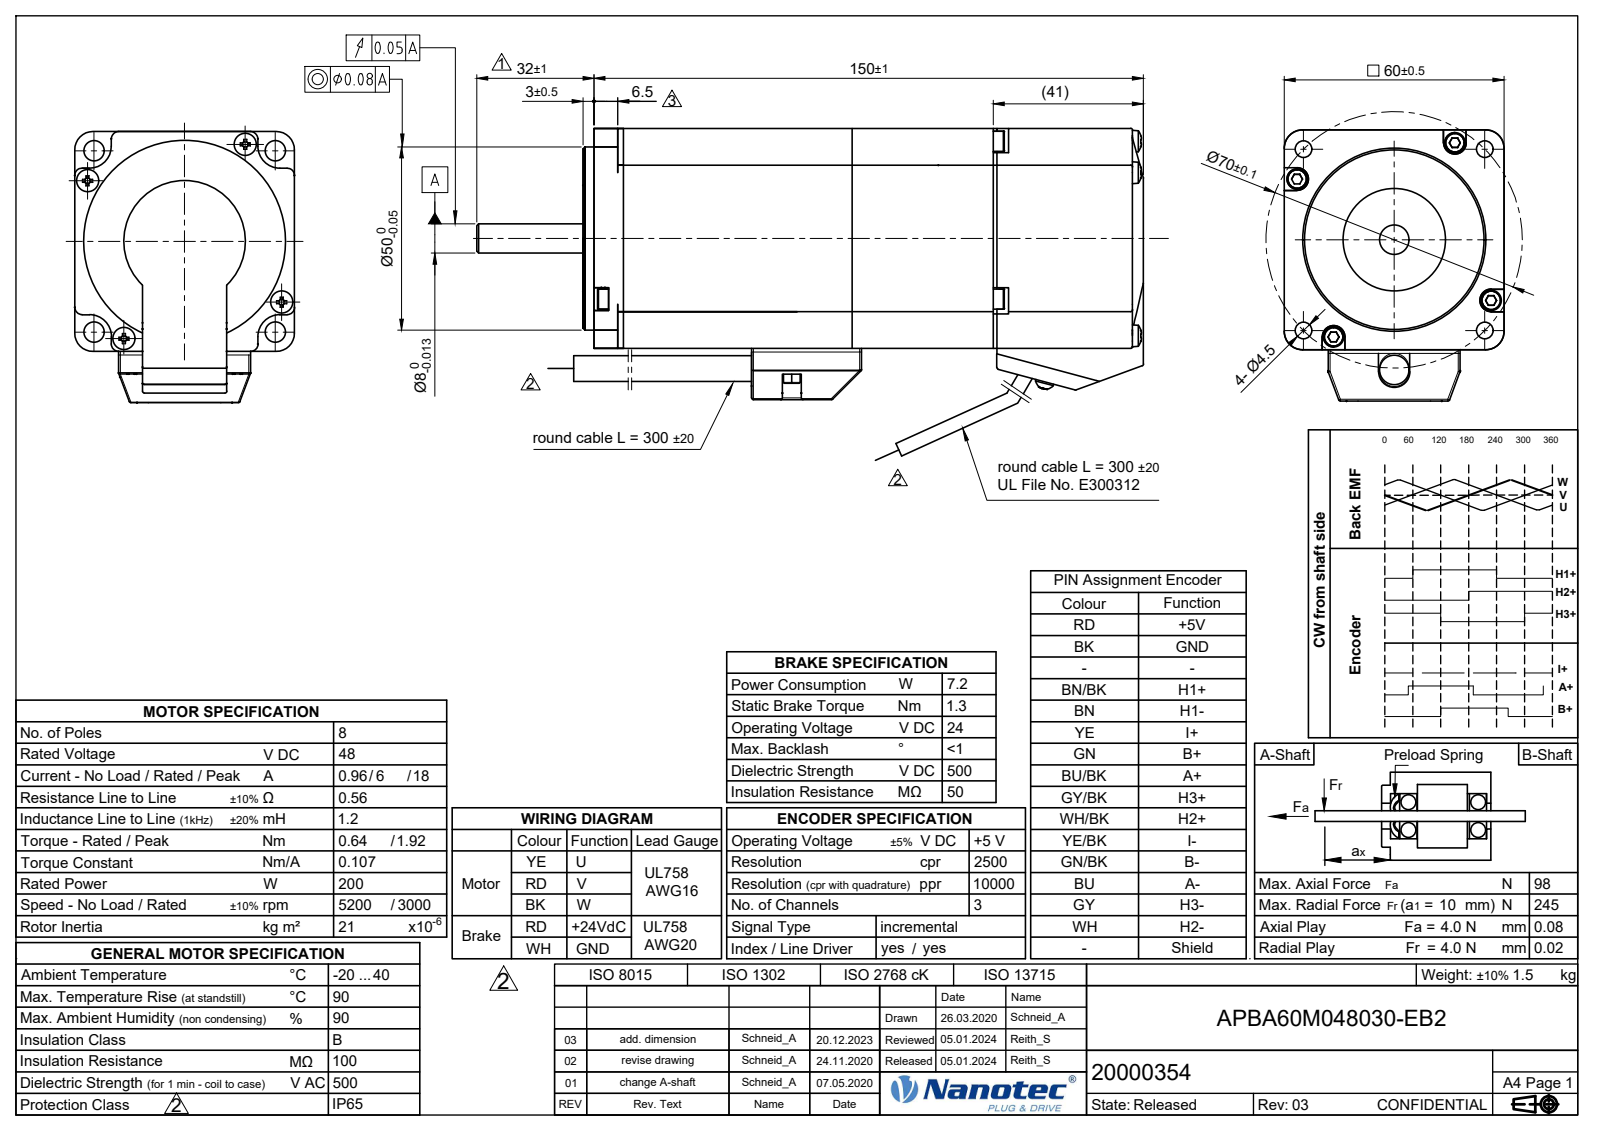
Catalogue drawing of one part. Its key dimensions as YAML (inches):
part_name: "APBA60M048030-EB2_Shrinkwrap_1"
step_written_by: "Autodesk Inventor 2019 (AUTOMOTIVE_DESIGN)"
units: inches
bodies: {solids: 29, faces: 1161, planar: 602, cylindrical: 352, other: 207}
overall_size: [7.165, 2.913, 2.362]
volume: 12.43
surface_area: 178.1
round_holes:
  - {diameter: 0.098, count: 19}
  - {diameter: 0.118, count: 15}
  - {diameter: 0.134, count: 8}
  - {diameter: 0.081, count: 4}
  - {diameter: 0.11, count: 4}
  - {diameter: 0.177, count: 4}
  - {diameter: 0.13, count: 3}
  - {diameter: 0.157, count: 3}
  - {diameter: 0.071, count: 2}
  - {diameter: 0.197, count: 1}
  - {diameter: 0.236, count: 1}
  - {diameter: 0.256, count: 1}
round_bosses_or_shafts:
  - {diameter: 0.217, count: 4}
  - {diameter: 0.108, count: 4}
  - {diameter: 0.177, count: 2}
  - {diameter: 0.118, count: 2}
  - {diameter: 0.098, count: 2}
  - {diameter: 0.089, count: 2}
  - {diameter: 2.205, count: 1}
  - {diameter: 0.748, count: 1}
partial_cylinders:
  - {radius: 0.02, count: 56}
  - {radius: 0.079, count: 18}
  - {radius: 0.197, count: 6}
  - {radius: 0.118, count: 5}
  - {radius: 0.122, count: 4}
  - {radius: 0.236, count: 4}
  - {radius: 0.157, count: 3}
  - {radius: 0.059, count: 2}
face_to_face_distances: [2.362, 1.575, 0.118, 0.098, 0.039, 0.236, 1.969, 1.614, 3.976, 0.394]
hole_center_spacings: [0.33, 1.23, 1.628, 1.74, 2.043, 2.592, 0.315, 0.487]
